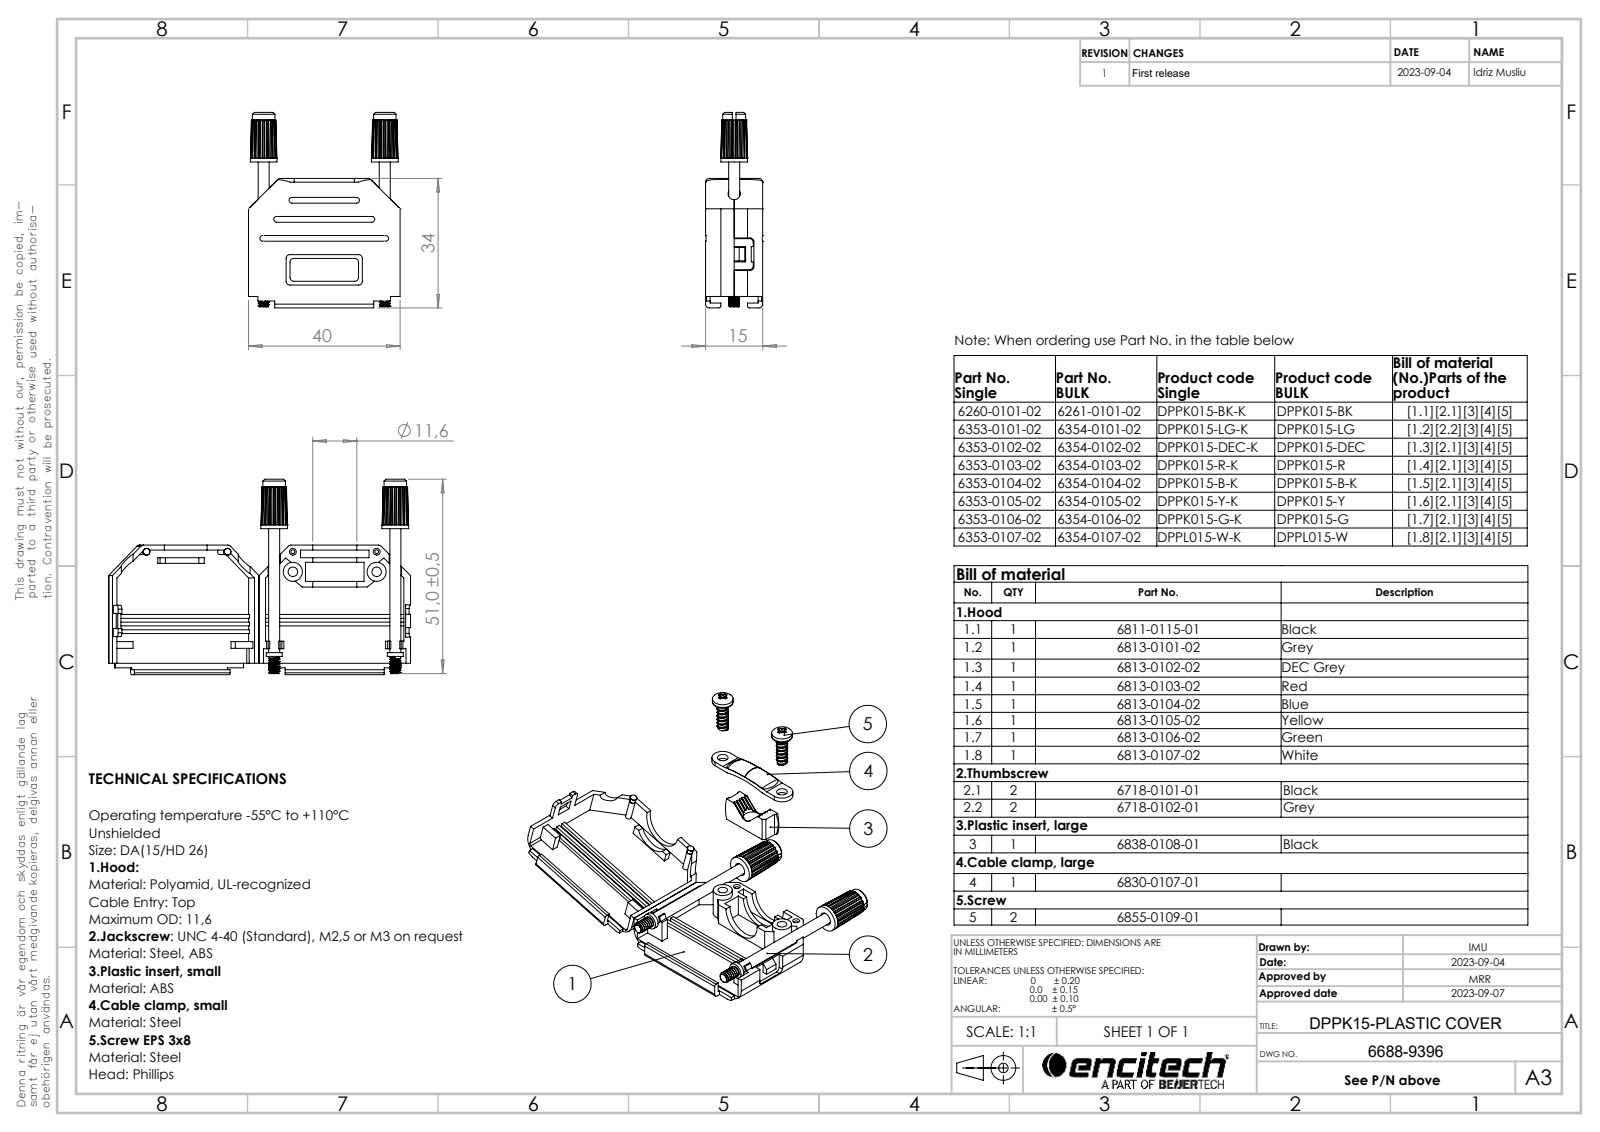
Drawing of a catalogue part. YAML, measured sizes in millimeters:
part_name: "Split1[2]; 6838-0108-01; 6261-0101-02 assembly part 1; 6261-0101-02 assembly part 2 (+8 more)"
step_written_by: "SolidWorks 2021 (AUTOMOTIVE_DESIGN)"
units: millimeters
bodies: {solids: 14, faces: 735, planar: 490, cylindrical: 138, other: 107}
overall_size: [51.3, 39.8, 15]
volume: 7564
surface_area: 11772
round_holes:
  - {diameter: 1, count: 2}
  - {diameter: 1.8, count: 2}
  - {diameter: 2.5, count: 2}
  - {diameter: 2.8, count: 2}
  - {diameter: 3.2, count: 2}
  - {diameter: 4.6, count: 1}
  - {diameter: 11.6, count: 1}
round_bosses_or_shafts:
  - {diameter: 7, count: 2}
  - {diameter: 6, count: 2}
  - {diameter: 5.45, count: 2}
  - {diameter: 5, count: 2}
  - {diameter: 4.2, count: 2}
  - {diameter: 3, count: 2}
  - {diameter: 2.9, count: 2}
partial_cylinders:
  - {radius: 1, count: 18}
  - {radius: 0.75, count: 8}
  - {radius: 0.2, count: 4}
  - {radius: 0.5, count: 4}
  - {radius: 4, count: 4}
  - {radius: 2, count: 3}
  - {radius: 2.85, count: 2}
  - {radius: 13.06, count: 2}
face_to_face_distances: [13.5, 1.5, 12, 1.2, 6, 15, 7.5, 1, 1.3, 2]
hole_center_spacings: [5.25, 15.9, 22, 22.62, 10.99, 11.01, 12.22, 12.24]
